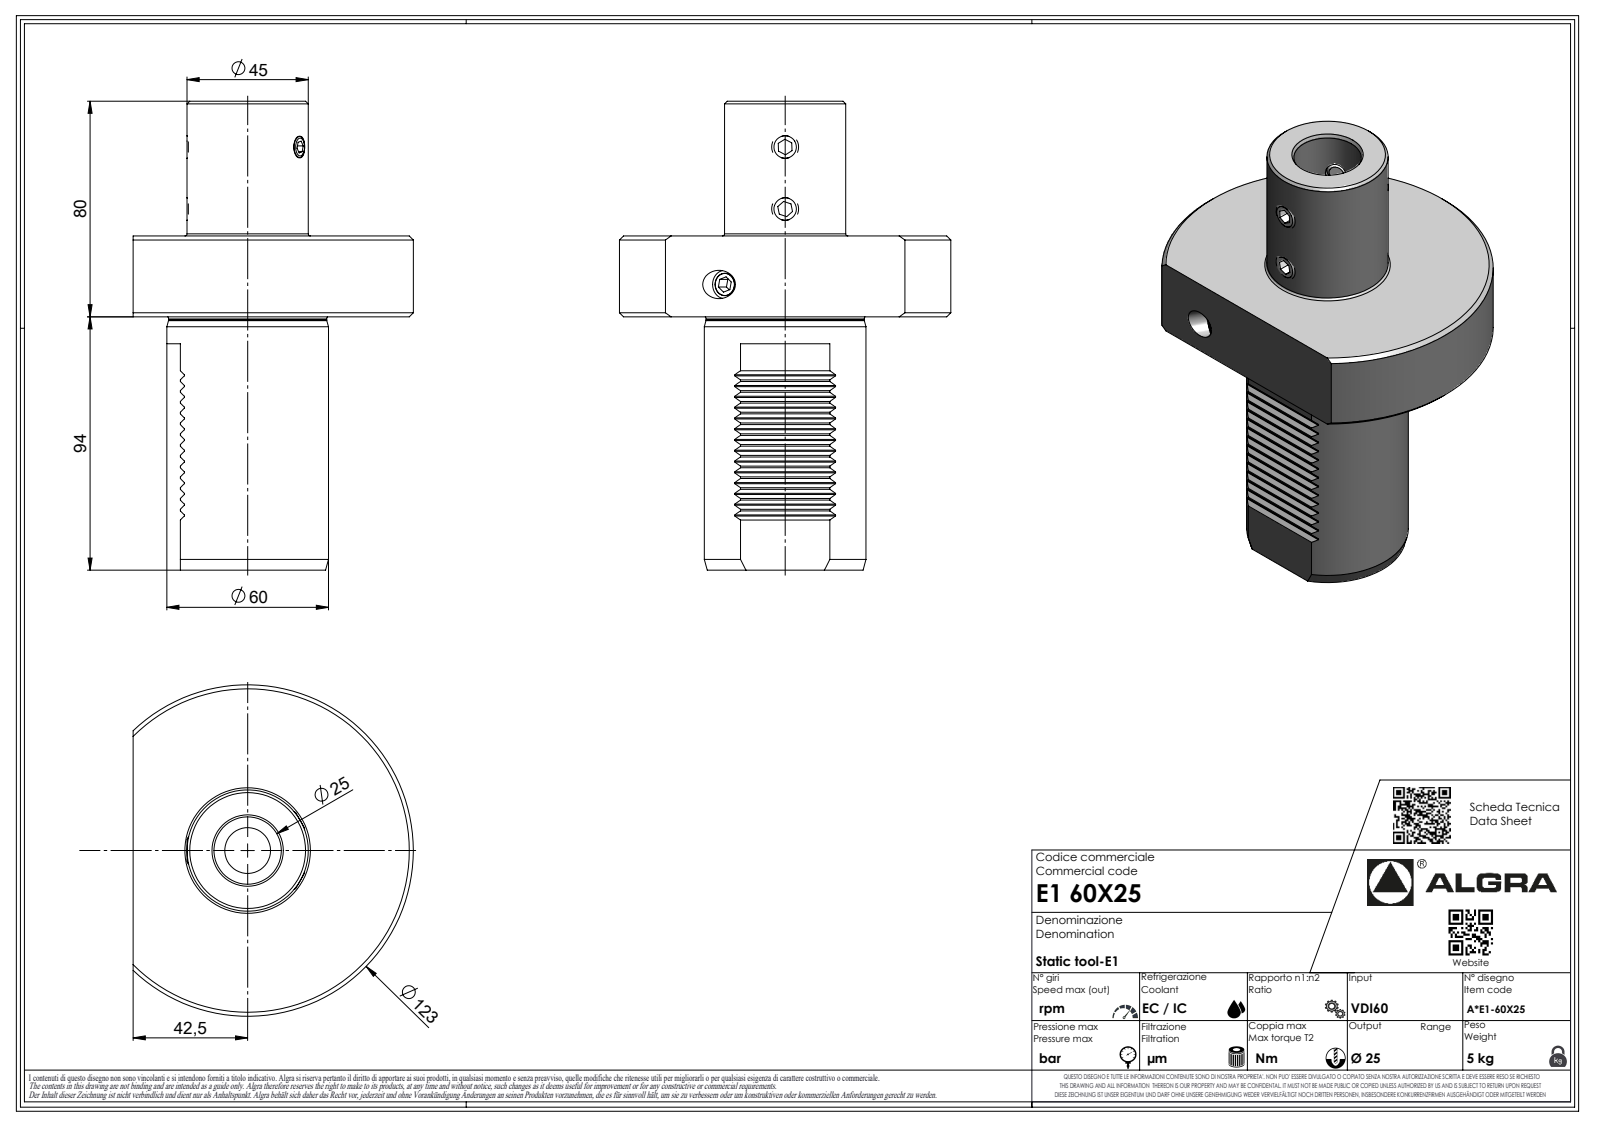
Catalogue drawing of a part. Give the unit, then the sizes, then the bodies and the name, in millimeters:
Units: millimetres
Overall size (bounding box): 174 × 123 × 104
Round holes (diameter × count): ⌀2.1 ×1, ⌀25 ×1
Round bosses / shafts (diameter × count): ⌀60 ×1, ⌀58.7 ×1, ⌀45 ×1, ⌀6.37 ×1, ⌀1.7 ×1
Partial cylindrical surfaces — rounded edges, fillets, slot ends (radius × count): R0.3 ×14, R0.33 ×7, R0.52 ×7, R3.7 ×7, R0.21 ×1, R61.5 ×1
Main face-to-face distances: 30, 94, 124, 2.83, 14.14, 11.31, 17.5, 8.48, 5.66, 174
Volume: 625 488 mm³ · Surface area: 61 998 mm²
Bodies: 1 solid, 283 faces (192 planar, 45 cylindrical, 46 other)
Part name (STEP PRODUCT): E160X25
STEP written by: SolidWorks 2023 (AUTOMOTIVE_DESIGN)
